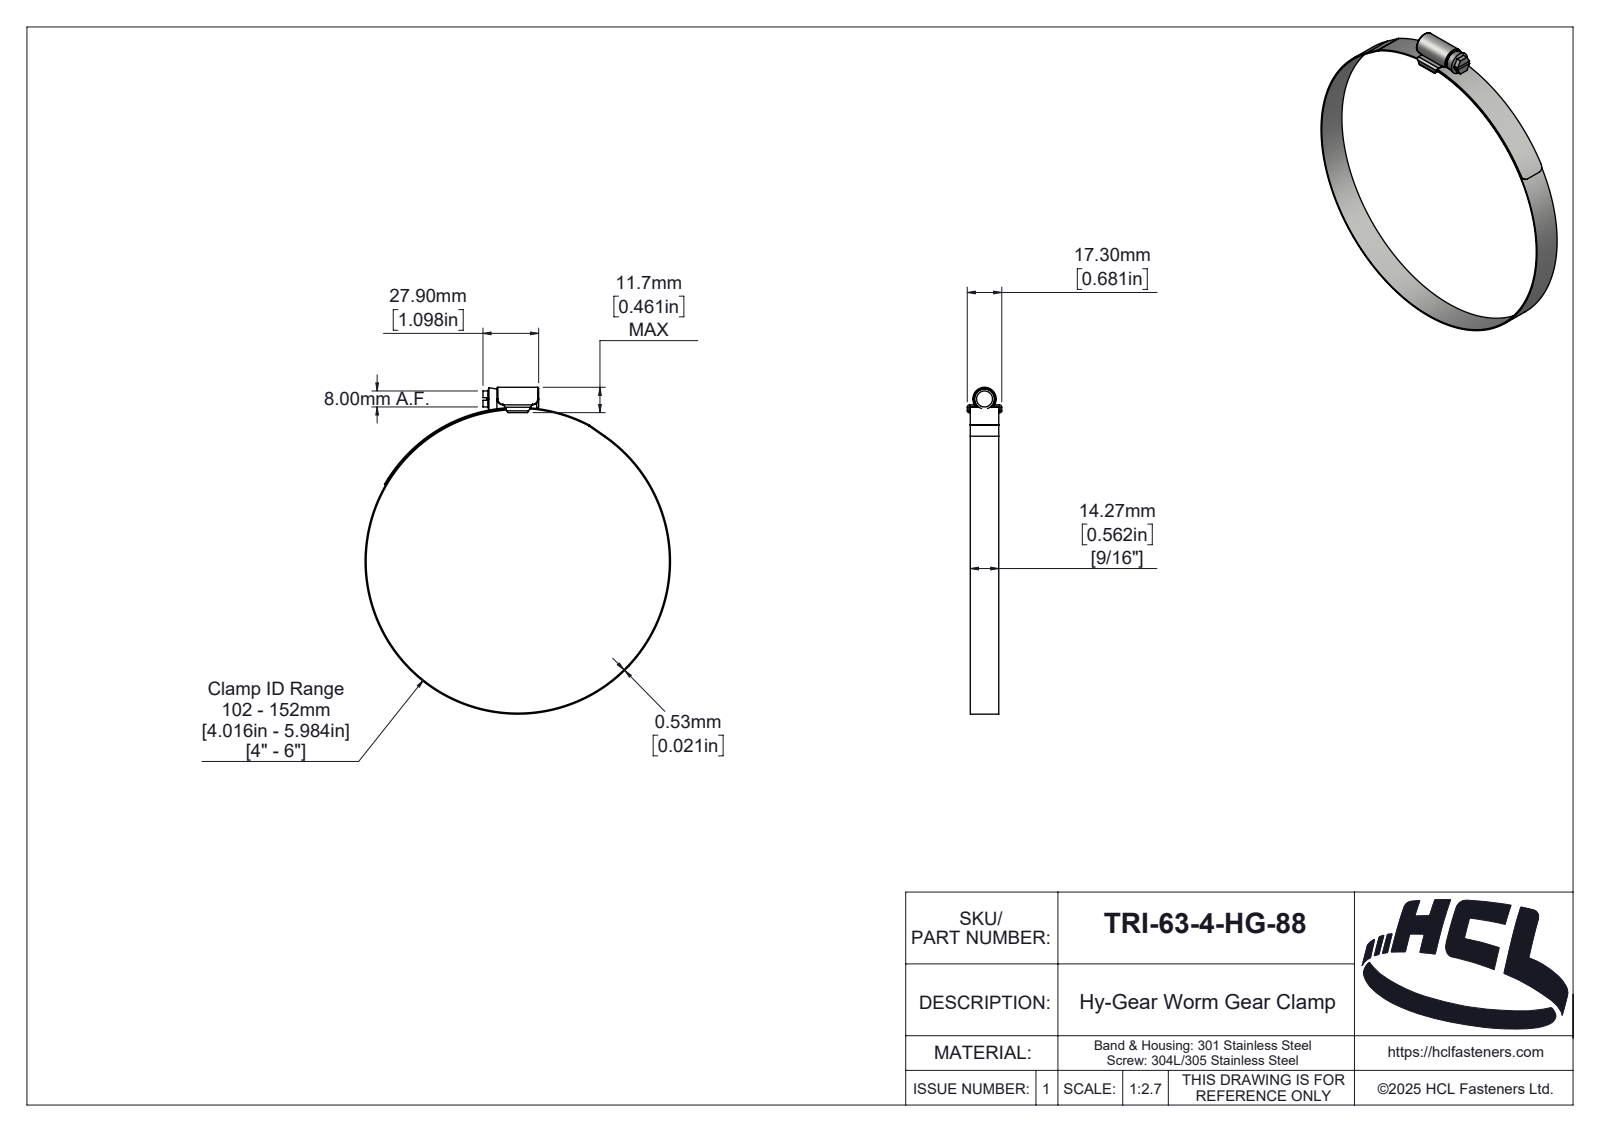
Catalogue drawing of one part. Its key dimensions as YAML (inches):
part_name: "TRI-50-0-HG-88"
step_written_by: "SolidWorks 2025 (AUTOMOTIVE_DESIGN)"
units: inches
bodies: {solids: 3, faces: 189, planar: 39, cylindrical: 89, other: 61}
overall_size: [6.446, 6.026, 0.681]
volume: 0.429
surface_area: 30.03
round_holes:
  - {diameter: 5.984, count: 1}
round_bosses_or_shafts:
  - {diameter: 6.026, count: 1}
  - {diameter: 0.394, count: 1}
partial_cylinders:
  - {radius: 0.02, count: 6}
  - {radius: 0.118, count: 4}
  - {radius: 0.004, count: 2}
  - {radius: 0.035, count: 2}
  - {radius: 0.047, count: 2}
  - {radius: 0.018, count: 1}
  - {radius: 0.074, count: 1}
  - {radius: 0.079, count: 1}
face_to_face_distances: [0.561, 0.031, 0.122, 0.021, 0.091, 0.154, 1.098, 0.06, 0.621, 0.65]
